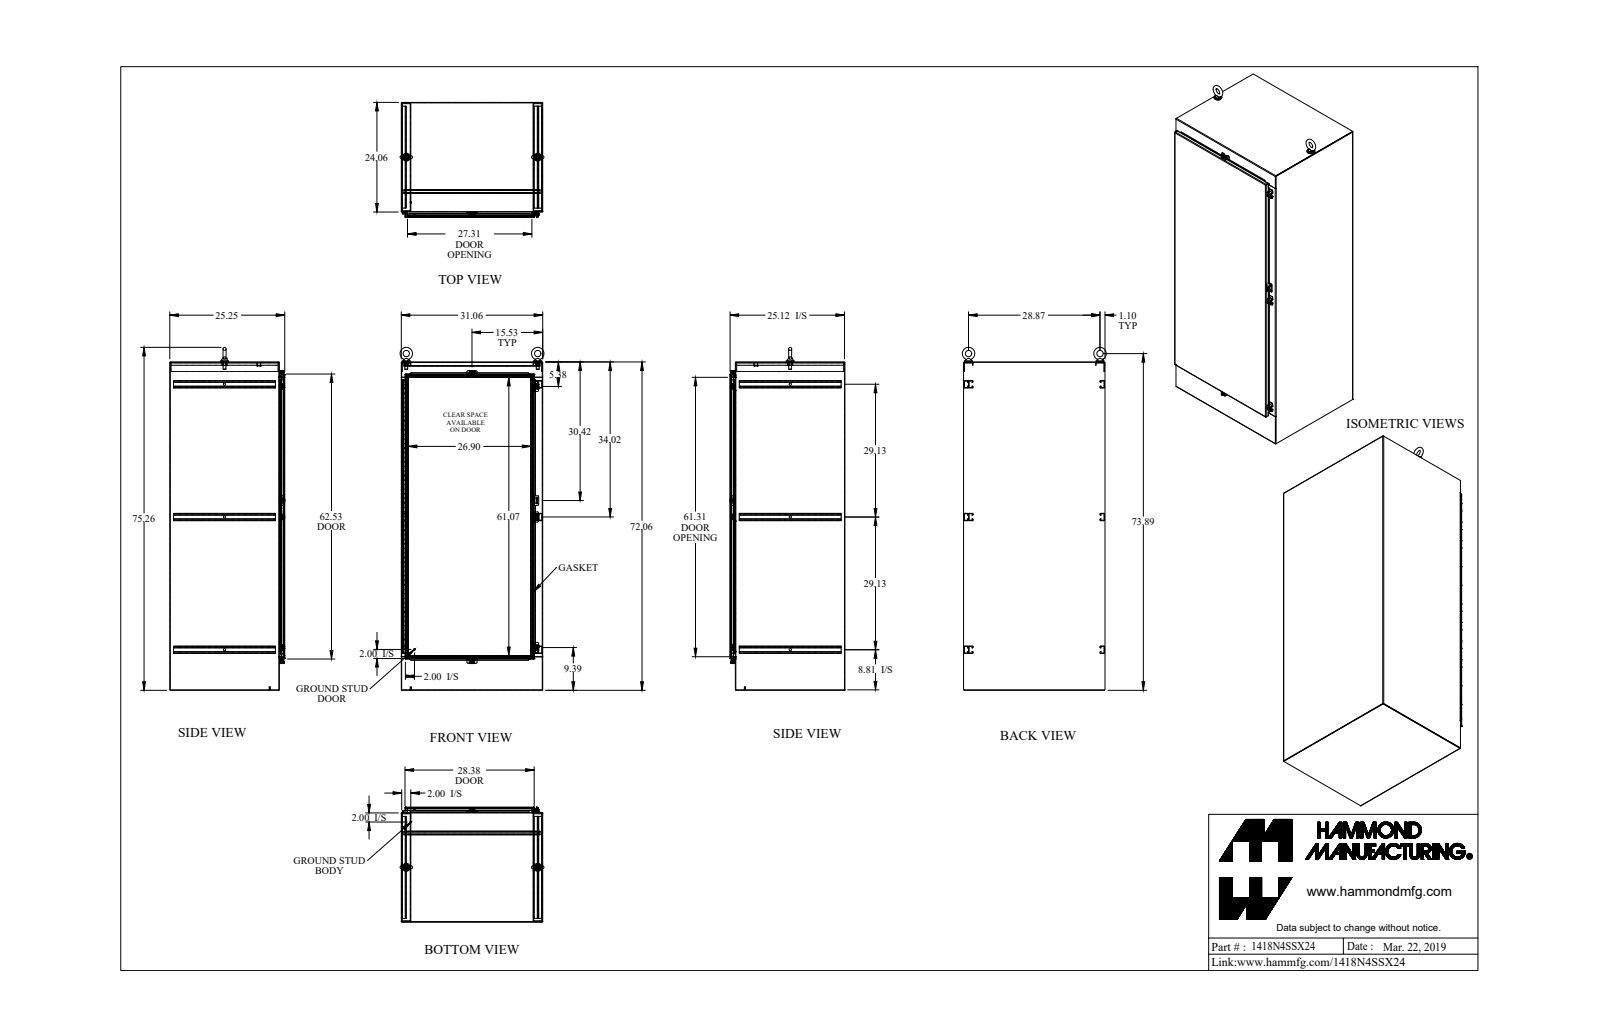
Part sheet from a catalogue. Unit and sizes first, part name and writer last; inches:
Units: inches
Overall size (bounding box): 75.719 × 32.118 × 25.31
Round holes (diameter × count): ⌀0.304 ×10, ⌀0.213 ×5, ⌀0.265 ×5, ⌀0.375 ×5, ⌀0.5 ×3, ⌀0.527 ×2, ⌀0.625 ×2, ⌀0.68 ×2, ⌀0.75 ×2, ⌀0.11 ×1, ⌀0.125 ×1
Round bosses / shafts (diameter × count): ⌀0.5 ×5, ⌀0.39 ×5, ⌀0.244 ×5, ⌀1.75 ×2, ⌀1.5 ×2, ⌀1.25 ×2, ⌀0.738 ×2, ⌀0.313 ×2
Partial cylindrical surfaces — rounded edges, fillets, slot ends (radius × count): R0.043 ×60, R0.138 ×54, R0.048 ×39, R0.143 ×39, R0.25 ×26, R0.06 ×10, R0.141 ×10, R0.125 ×8
Main face-to-face distances: 0.095, 25.15, 30.965, 30.87, 25.055, 25.245, 31.06, 71.965, 1.185, 23.965
Hole centre spacings: 6, 12, 18, 24, 30, 36, 42, 29.13
Volume: 1 074 in³ · Surface area: 22 774 in²
Bodies: 52 solids, 1734 faces (1076 planar, 574 cylindrical, 84 other)
Part name (STEP PRODUCT): 1418N4SSX24
STEP written by: SolidWorks 2019 (AUTOMOTIVE_DESIGN)
